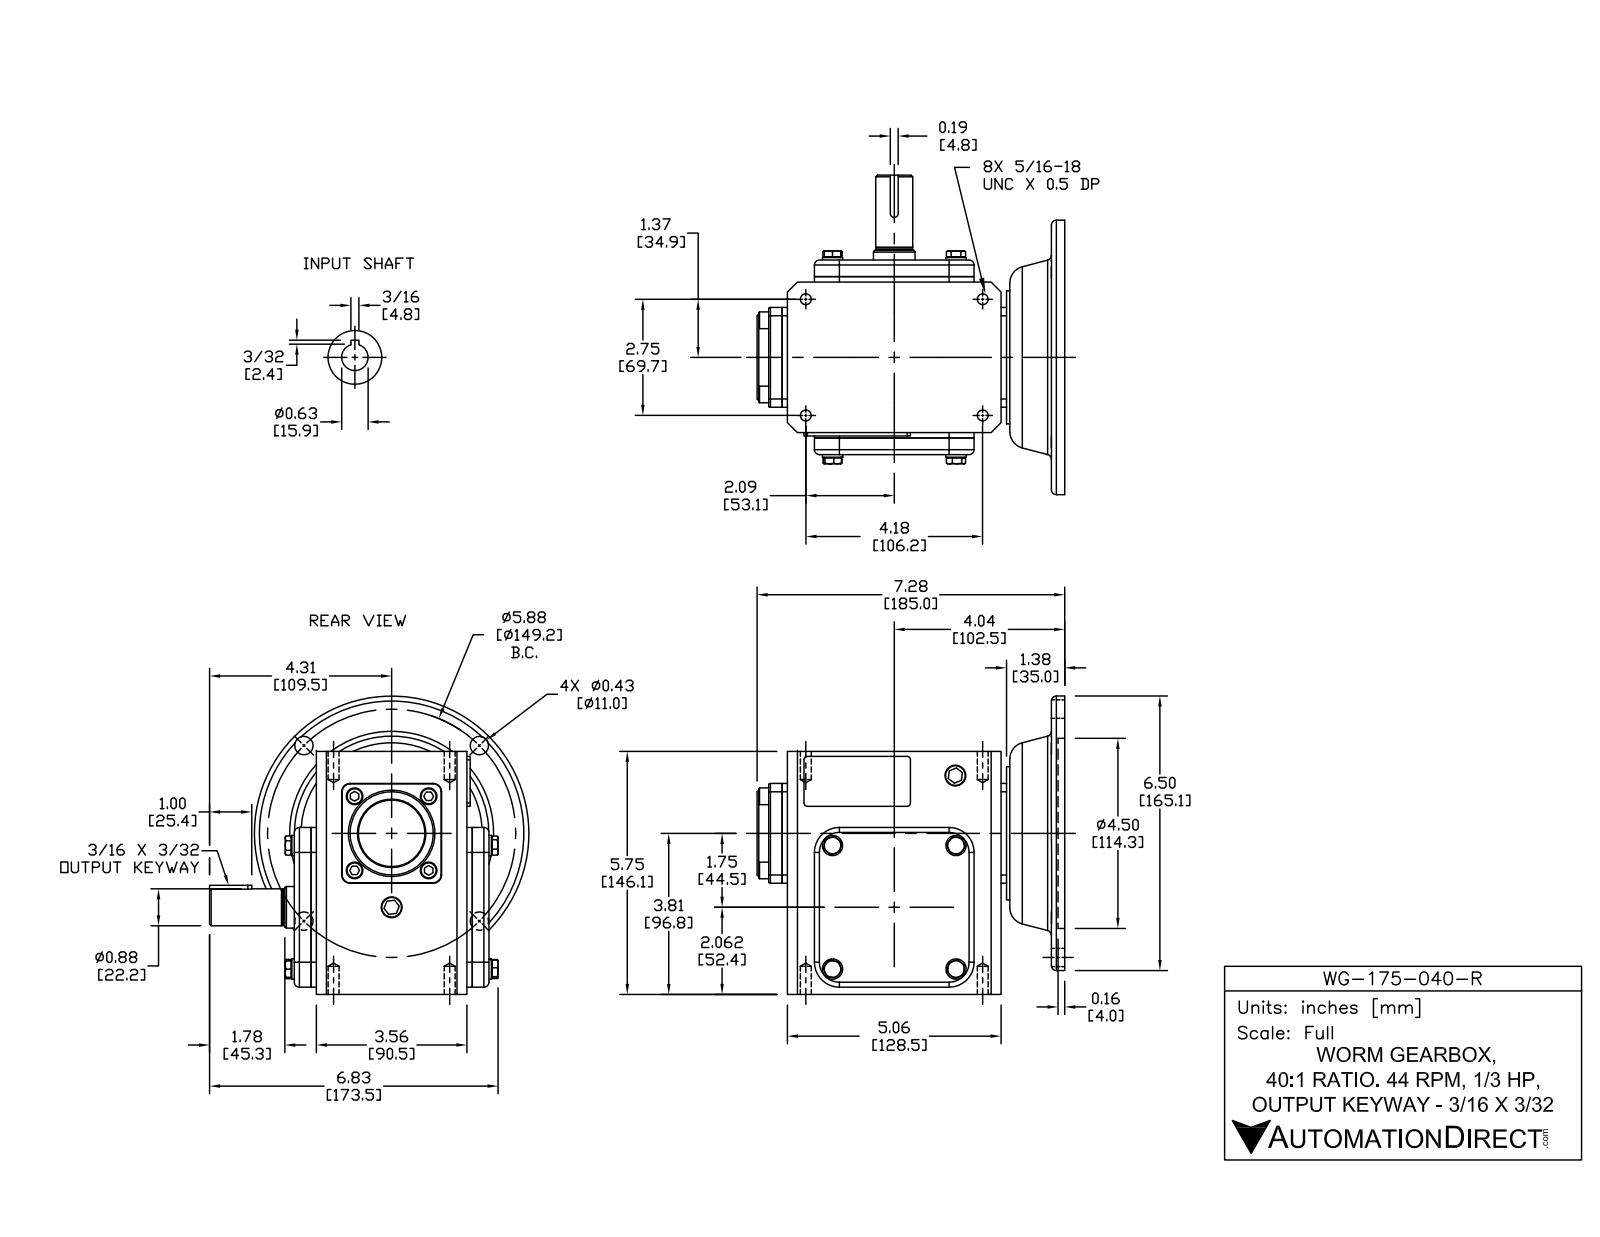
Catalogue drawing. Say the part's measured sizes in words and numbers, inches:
The part is named "WG-175-040-R". Its 3-D file was written by "SolidWorks 2015 (CONFIG_CONTROL_DESIGN)". It is 43 solids with 613 faces: 312 planar, 172 cylindrical and 129 other. Overall it measures 7.559 by 7.283 by 7.06 inches. Its volume is 131.9 cubic inches and its surface area 366.4 square inches. Round holes: 4 of diameter 0.257, 4 of diameter 0.406, 1 of diameter 0.512, 1 of diameter 0.625, 1 of diameter 0.984, 1 of diameter 1.181, 1 of diameter 1.457, 1 of diameter 1.575, 1 of diameter 3.543, 1 of diameter 4.5. Round bosses or shafts: 8 of diameter 0.394, 4 of diameter 0.48, 2 of diameter 0.512, 1 of diameter 6.496, 1 of diameter 3.15, 1 of diameter 2.047, 1 of diameter 1.575, 1 of diameter 0.875. Partial cylindrical surfaces (rounded edges, fillets, slot ends): 8 of radius 0.079, 8 of radius 0.118, 4 of radius 0.197, 4 of radius 0.591, 2 of radius 0.02, 2 of radius 0.039, 1 of radius 0.094. The main face-to-face distances are 0.128, 3.819, 4.213, 0.394, 4.085, 3.691, 0.522, 0.315, 5.75, 6.693. The hole center spacings are 2.937, 4.154, 2.103, 2.75, 4.188, 4.354, 5.01, 5.875.
